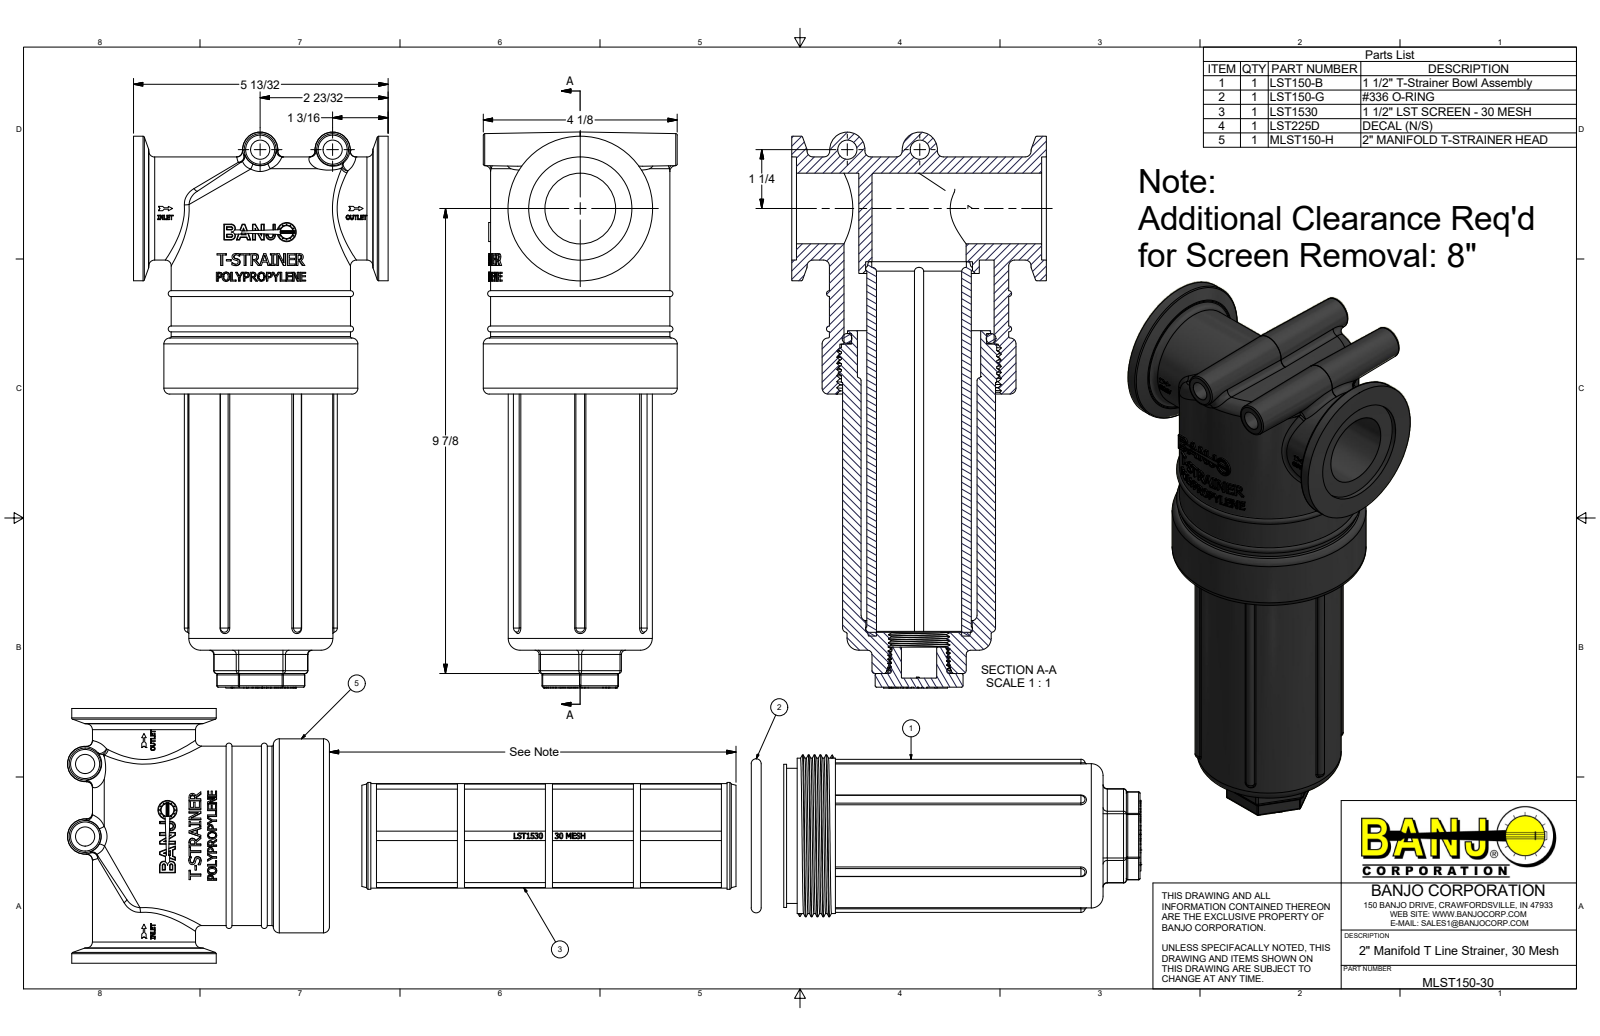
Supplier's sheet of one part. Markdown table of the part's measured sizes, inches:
| quantity | value |
| --- | --- |
| part name | MLST150-30; MLST150-H; LST150-B; LST150-XB (+4 more) |
| STEP written by | Autodesk Inventor 2019 (AUTOMOTIVE_DESIGN) |
| units | inches |
| bodies | 6 solids, 2179 faces (1183 planar, 235 cylindrical, 761 other) |
| overall size | 21.929 × 5.41 × 4.12 |
| volume | 52.11 in³ |
| surface area | 582.4 in² |
| round holes (diameter × count) | 0.406 × 2, 0.272 × 1, 0.385 × 1, 0.75 × 1, 1.5 × 1, 1.81 × 1, 1.97 × 1, 2 × 1, 2.26 × 1, 3.19 × 1, 3.365 × 1 |
| round bosses / shafts (diameter × count) | 4.12 × 1, 3.81 × 1, 3.435 × 1, 3.3 × 1, 3.07 × 1, 3.04 × 1, 2.87 × 1, 2.56 × 1 |
| partial cylindrical surfaces (radius × count) | 0.03 × 18, 0.06 × 13, 0.09 × 6, 0.1 × 5, 0.024 × 2, 0.034 × 2, 0.079 × 2, 0.089 × 2 |
| main face-to-face distances | 0.1, 5.31, 5.41, 1.24, 2.805, 0.92, 3.63, 6.12, 9.75, 1.87 |
| hole center spacings | 1.54, 1.838, 2.004 |
